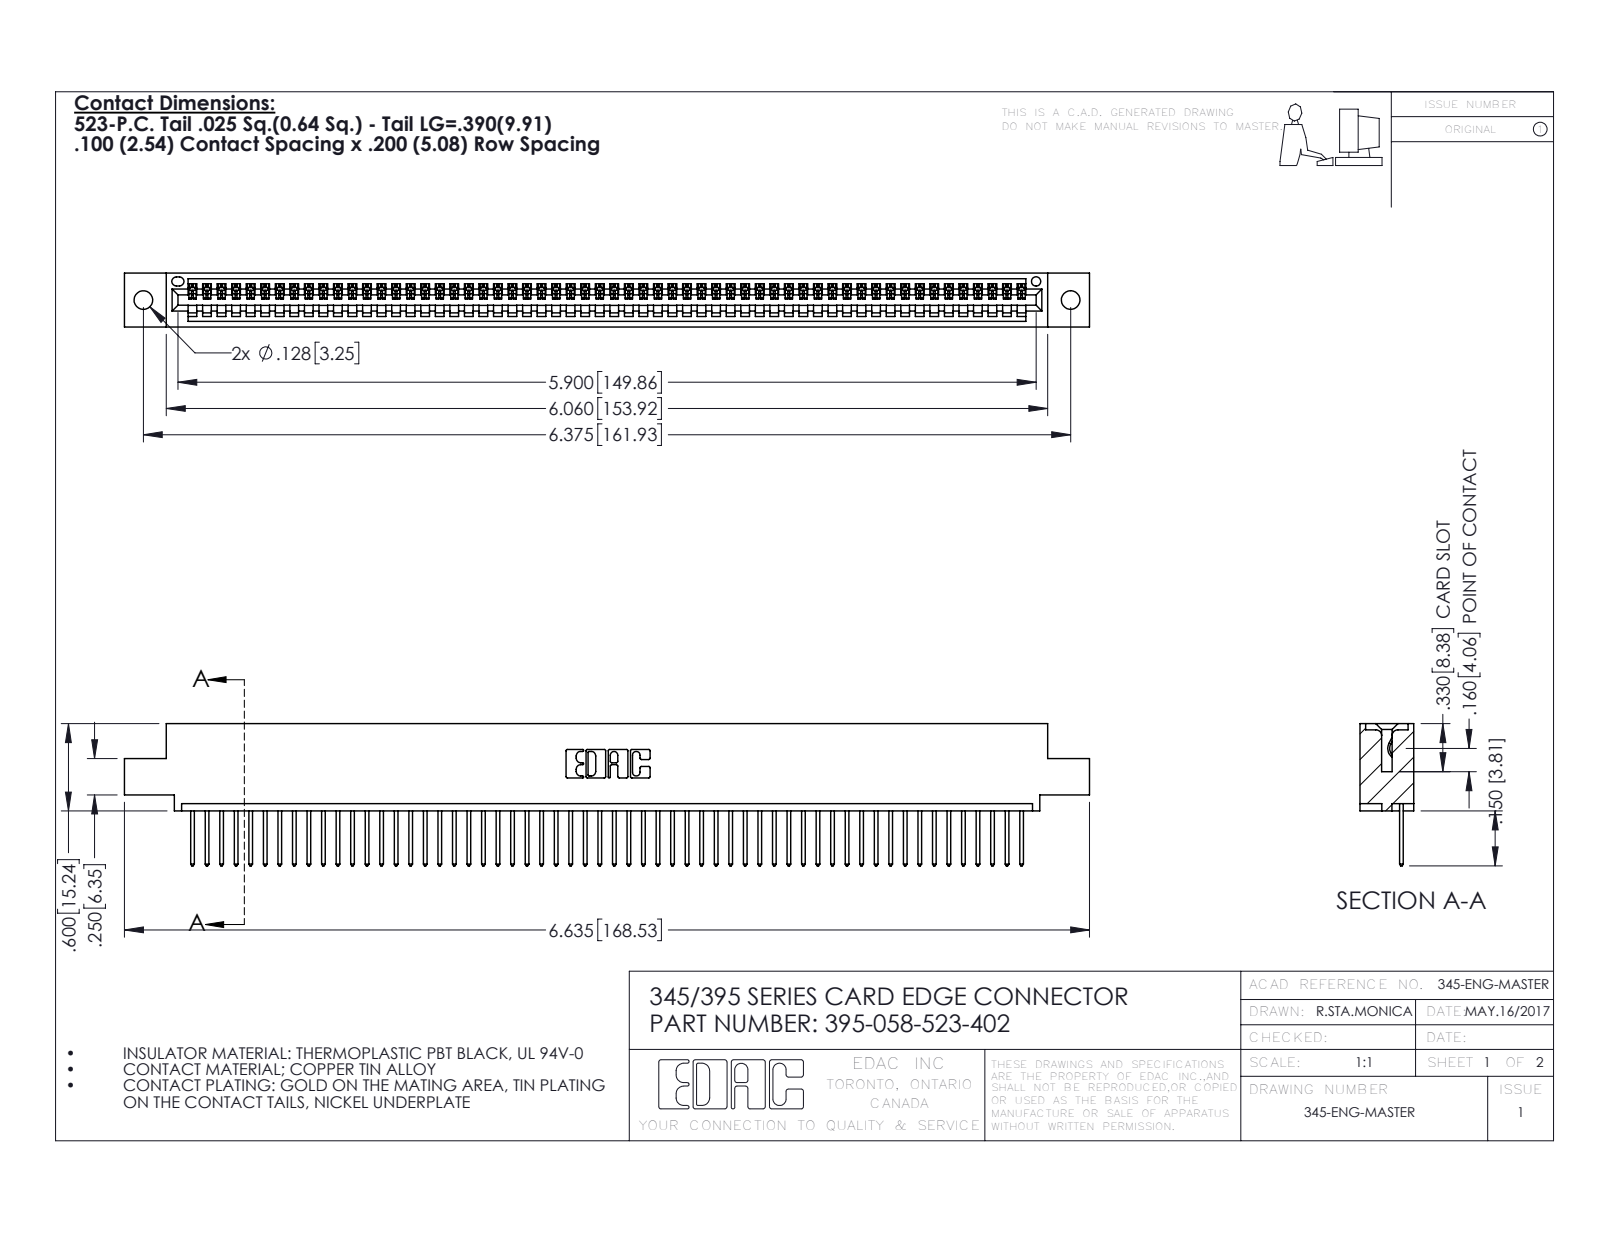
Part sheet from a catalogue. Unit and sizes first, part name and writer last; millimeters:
Units: millimetres
Overall size (bounding box): 168.5 × 24.8 × 9.4
Round holes (diameter × count): ⌀3.3 ×2, ⌀1.6 ×1
Partial cylindrical surfaces — rounded edges, fillets, slot ends (radius × count): R0.2 ×116, R0.3 ×116, R0.3 ×22, R0.2 ×6, R0.8 ×6, R0.7 ×3, R0.8 ×2, R1 ×2
Main face-to-face distances: 7.6, 1.8, 9.4, 2.5, 6.9, 0.6, 5.1, 5.7, 3.8, 1.8
Hole centre spacings: 6.9, 155.9, 161.9
Volume: 16 000 mm³ · Surface area: 21 360 mm²
Bodies: 59 solids, 3494 faces (2404 planar, 1090 cylindrical, 0 other)
Part name (STEP PRODUCT): 395-058-523-402; 345-292-001_345-293-123; 345 Part_0.110 Offset - 0.128 Dia
STEP written by: SolidWorks 2016 (CONFIG_CONTROL_DESIGN)
